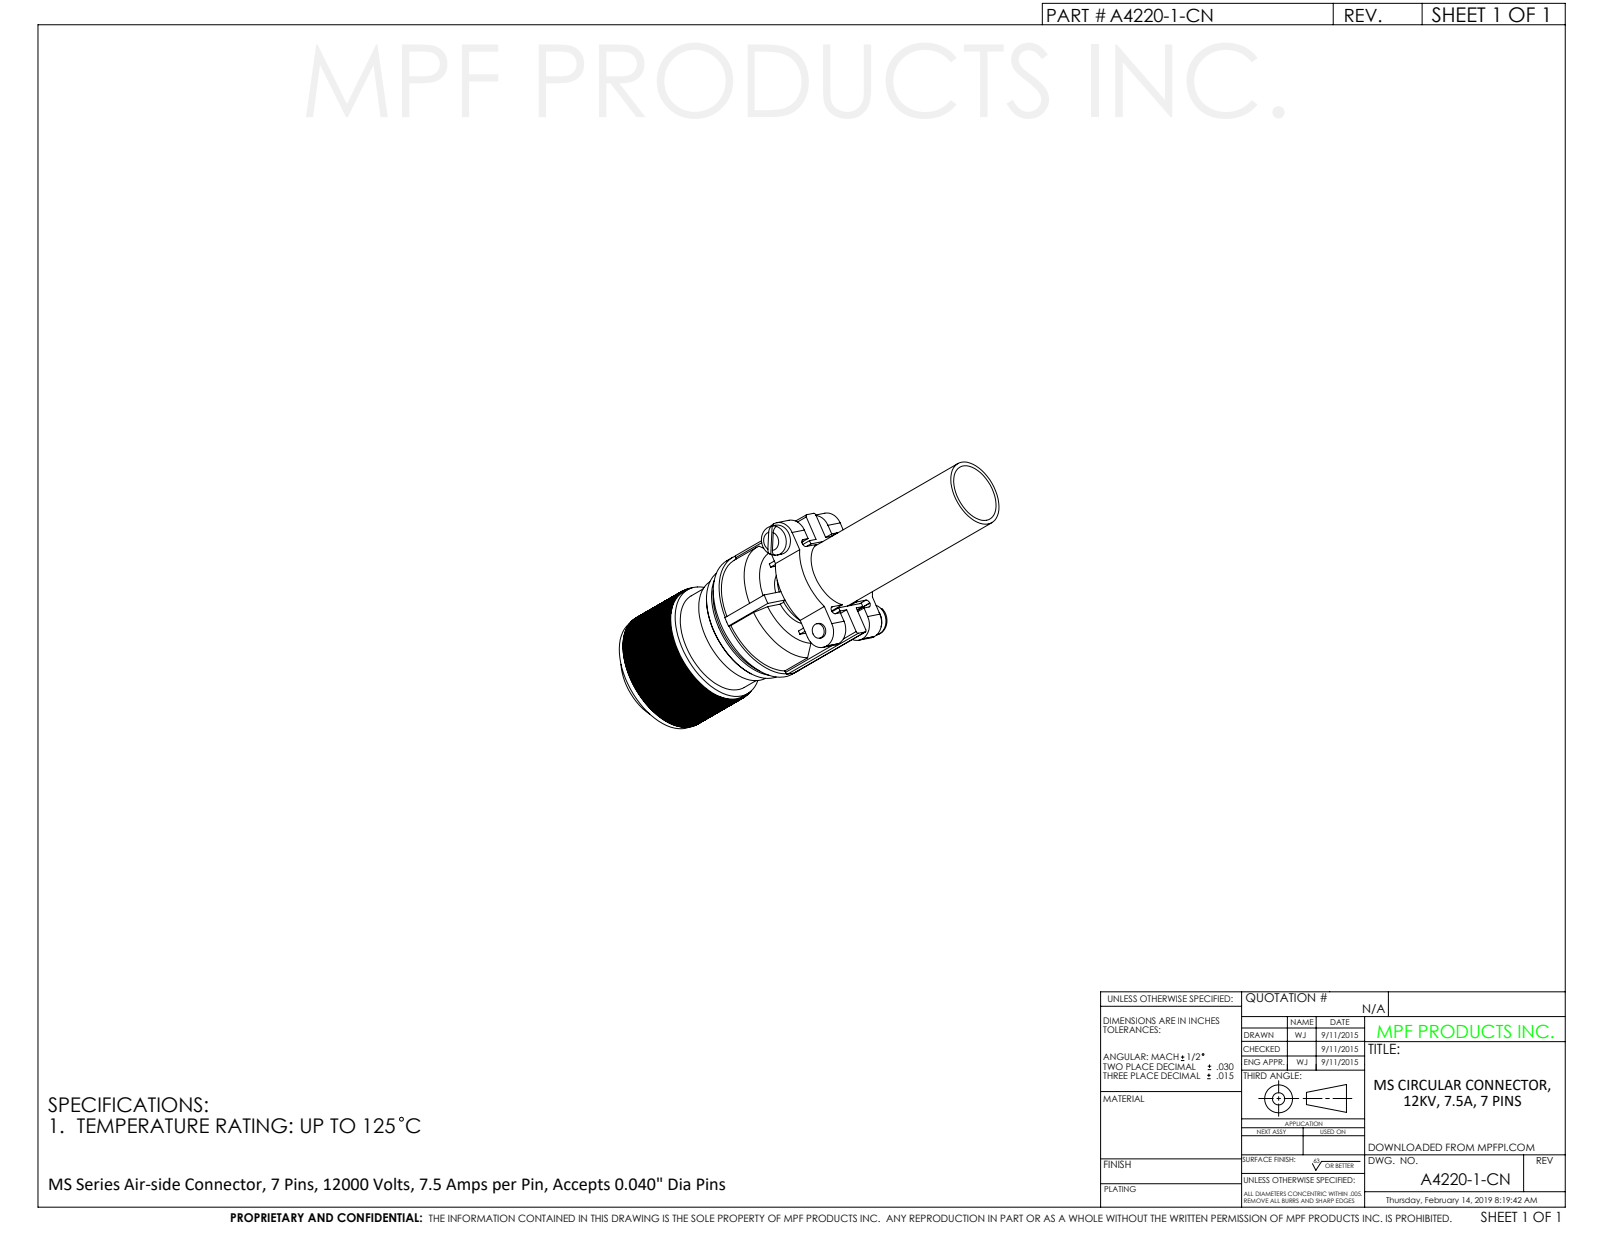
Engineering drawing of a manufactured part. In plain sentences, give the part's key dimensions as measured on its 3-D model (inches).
The part is named "A4220-1-CN; A4216_A4216-3; A4219; 97-3057-1008-1 (676) (+1 more)". Its 3-D file was written by "SolidWorks 2012 (CONFIG_CONTROL_DESIGN)". It is 9 solids with 1141 faces: 215 planar, 447 cylindrical and 479 other. Overall it measures 3.797 by 1.532 by 1.319 inches. Its volume is 1.132 cubic inches and its surface area 46.3 square inches. Round holes: 7 of diameter 0.031, 7 of diameter 0.046, 7 of diameter 0.068, 7 of diameter 0.098, 7 of diameter 0.12, 7 of diameter 0.154, 5 of diameter 0.045, 5 of diameter 0.055, 2 of diameter 0.045, 2 of diameter 0.055, 1 of diameter 0.55, 1 of diameter 0.663. Round bosses or shafts: 7 of diameter 0.118, 7 of diameter 0.1, 7 of diameter 0.08, 7 of diameter 0.078, 7 of diameter 0.053, 6 of diameter 0.12, 2 of diameter 0.135, 1 of diameter 1.2. Partial cylindrical surfaces (rounded edges, fillets, slot ends): 8 of radius 0.034, 7 of radius 0.156, 4 of radius 0.02, 1 of radius 0.323, 1 of radius 0.472, 1 of radius 0.473. The main face-to-face distances are 0.278, 0.653, 0.375, 0.15, 0.748, 0.47, 0.095, 0.525, 0.3, 1.269. The hole center spacings are 0.204, 0.407, 0.352, 0.347, 0.357, 0.194, 0.203, 0.212.
